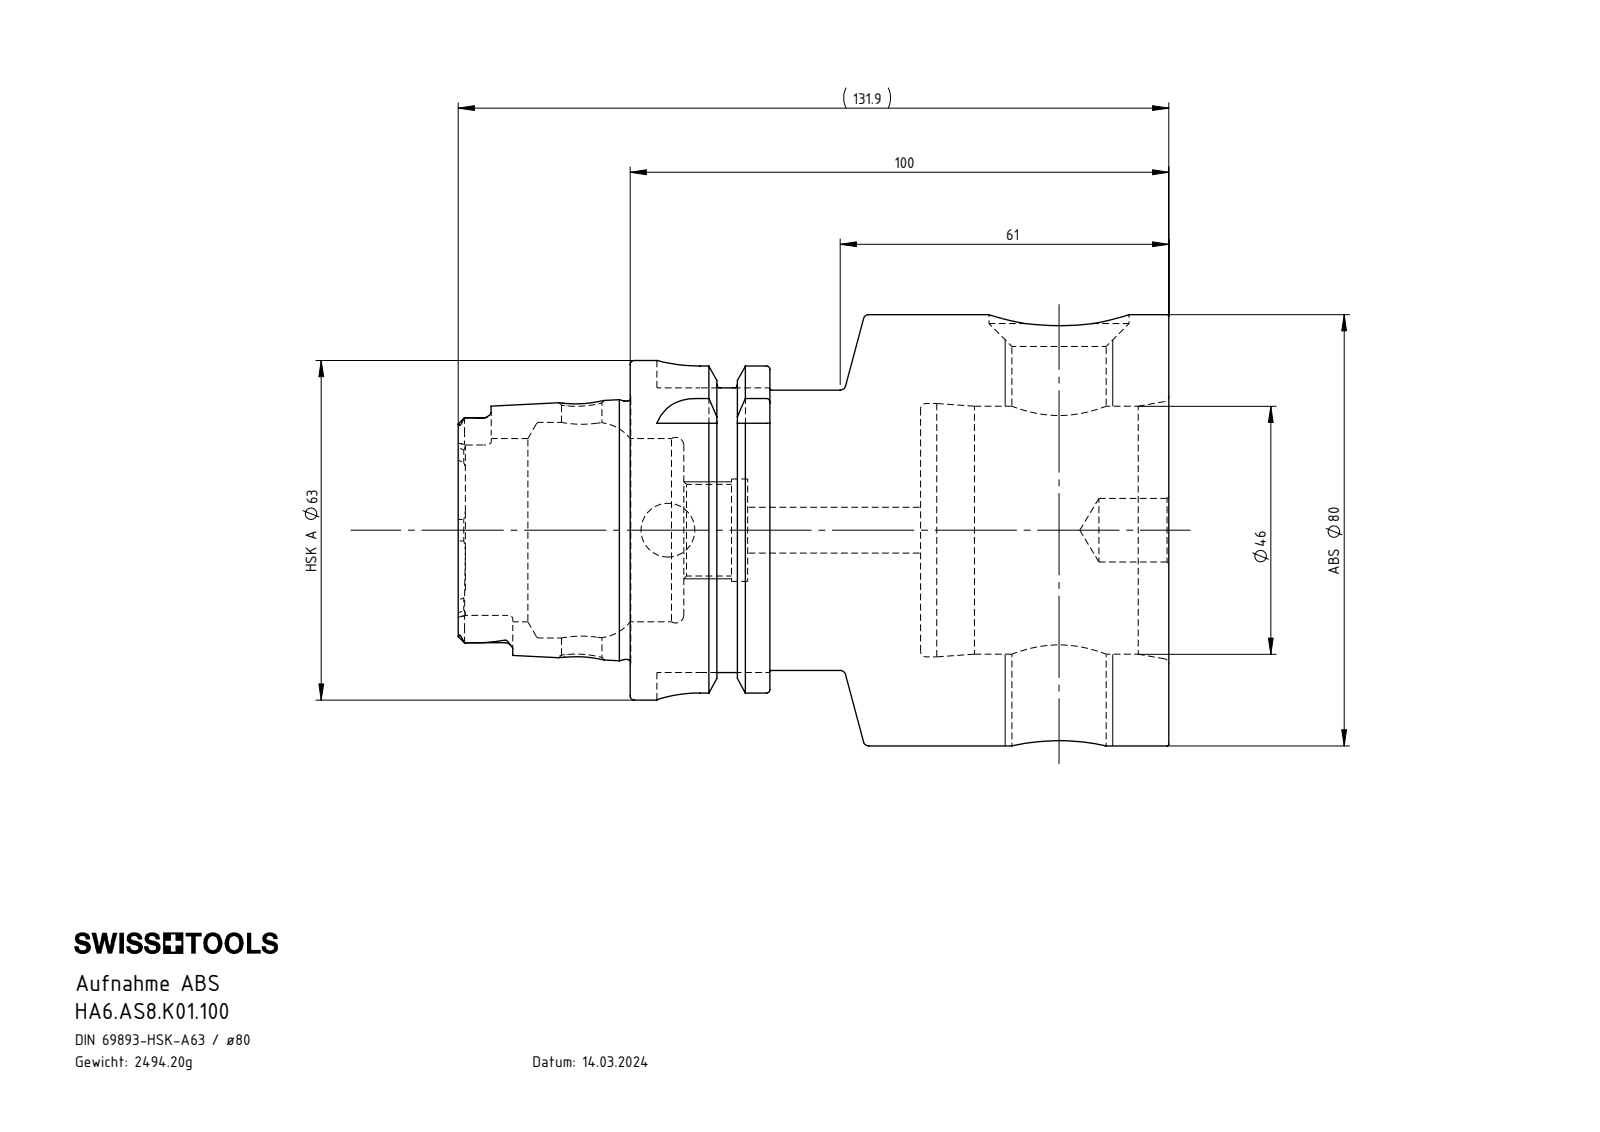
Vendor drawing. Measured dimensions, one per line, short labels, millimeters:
name: HA6.AS8.K01.100
written by: SolidWorks 2022 (AUTOMOTIVE_DESIGN)
unit: mm
bodies: 1 solid, 200 faces (47 planar, 60 cylindrical, 93 other)
size: 131.9 × 80 × 80
volume: 317 729 mm³; area: 52 971 mm²
holes: 1× ⌀7.5, 1× ⌀8.5, 1× ⌀10, 1× ⌀11.8, 1× ⌀17, 1× ⌀17.5, 1× ⌀19, 1× ⌀34, 1× ⌀40, 1× ⌀46, 1× ⌀47
bosses: 1× ⌀80, 1× ⌀63, 1× ⌀54.95, 1× ⌀52, 1× ⌀47.94
rounds: 6× R1.4, 4× R2.88, 4× R8, 1× R13
face distances: 46.1, 53.9, 100, 25.95, 27.95, 74.05, 16, 9.95, 43.95, 90.05
hole spacings: 31, 88.6
